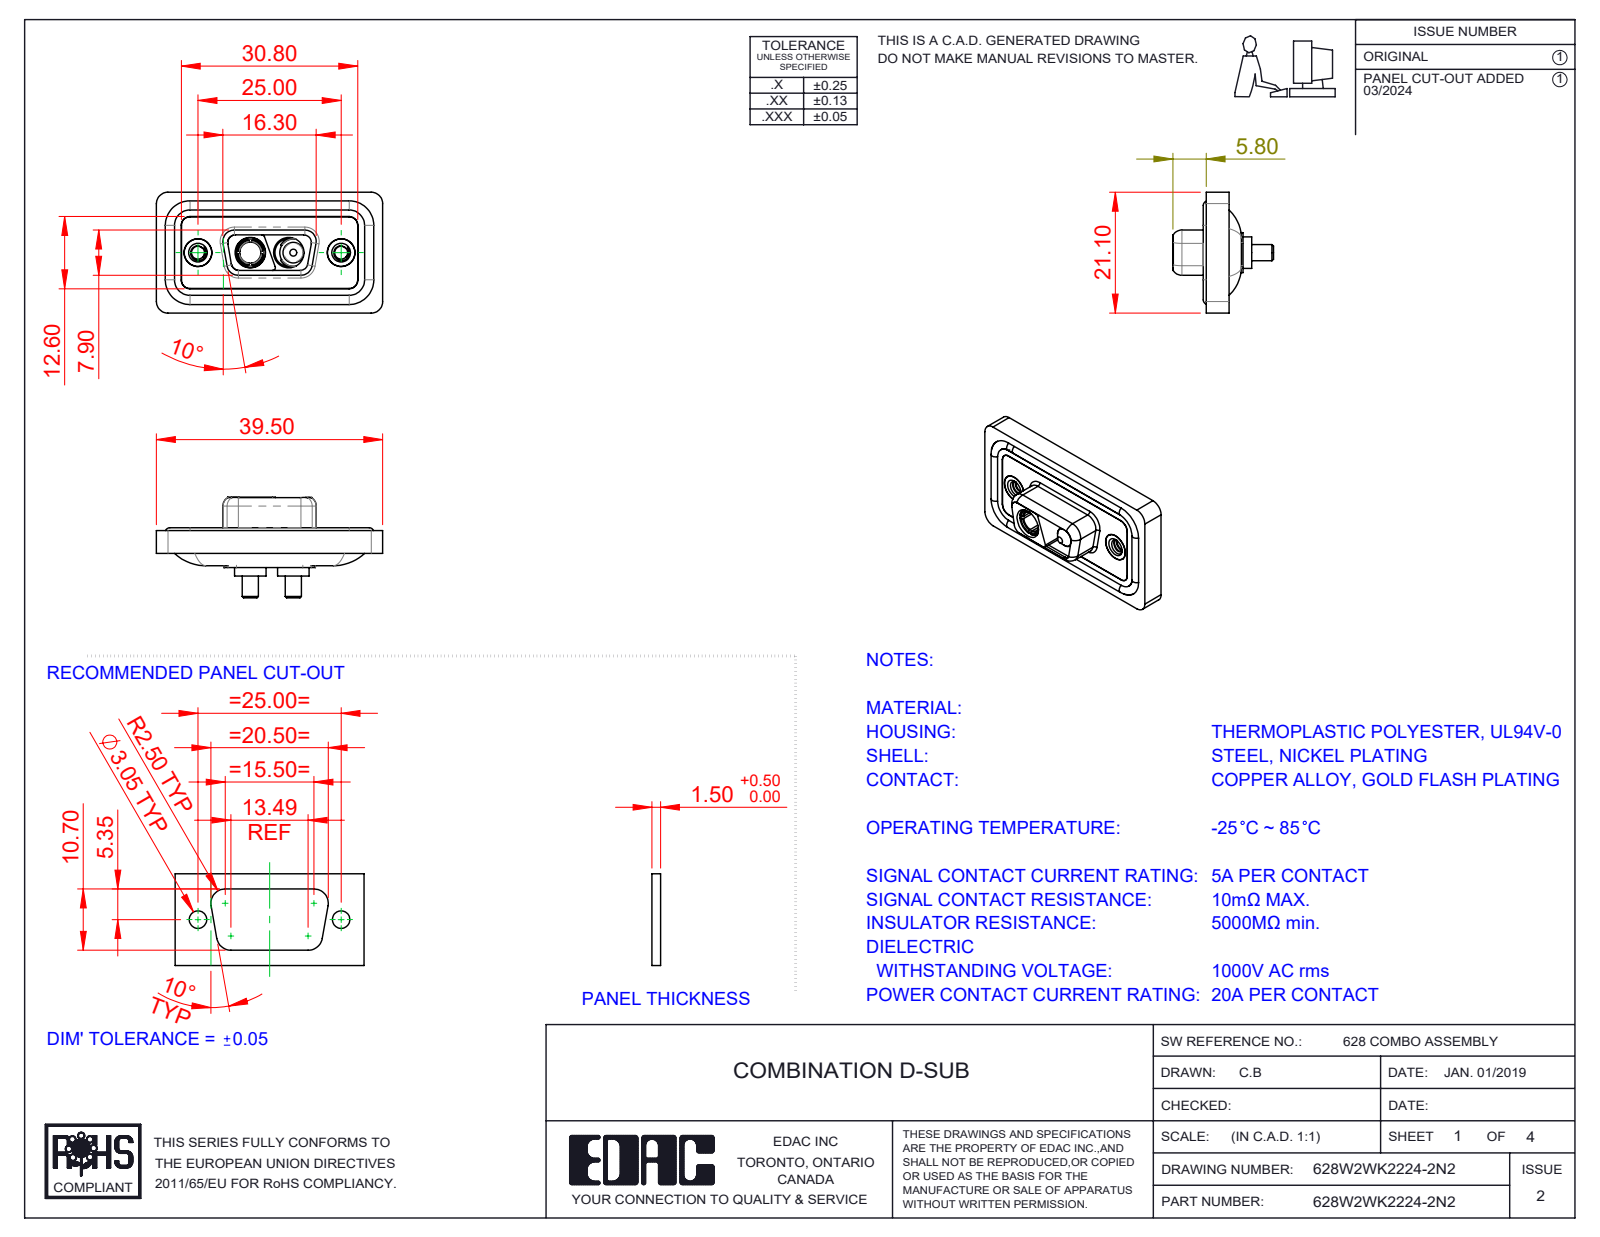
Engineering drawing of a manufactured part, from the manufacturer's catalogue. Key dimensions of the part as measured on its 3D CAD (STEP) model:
Part name (STEP PRODUCT): 628Combo Housing_2WK2; 628Combo Threaded Rivet_2; Power Pin_20A S; 628Combo Shell Rear_09 Contacts (+4 more)
STEP written by: SolidWorks 2023 (CONFIG_CONTROL_DESIGN)
Units: millimetres
Bodies: 11 solids, 500 faces (144 planar, 231 cylindrical, 125 other)
Overall size (bounding box): 39.5 × 21.1 × 17.55
Volume: 4 603 mm³ · Surface area: 7 344 mm²
Round holes (diameter × count): ⌀4.85 ×4, ⌀2.26 ×2, ⌀4 ×2, ⌀4.05 ×2, ⌀5 ×2, ⌀5.3 ×2, ⌀3.7 ×1
Round bosses / shafts (diameter × count): ⌀1.6 ×4, ⌀5.5 ×2, ⌀5.2 ×2, ⌀4.95 ×2, ⌀4.8 ×2, ⌀4.75 ×2, ⌀3.75 ×2, ⌀2.8 ×2
Partial cylindrical surfaces — rounded edges, fillets, slot ends (radius × count): R1.5 ×22, R2 ×18, R1.35 ×8, R1.6 ×8, R0.5 ×6, R0.25 ×4, R0.6 ×4, R0.65 ×4
Main face-to-face distances: 0.4, 1.1, 2.9, 1.6, 0.5, 1.8, 5.65, 1.5, 5.35, 3.1
Hole centre spacings: 9.14, 15.86, 6.72, 25
